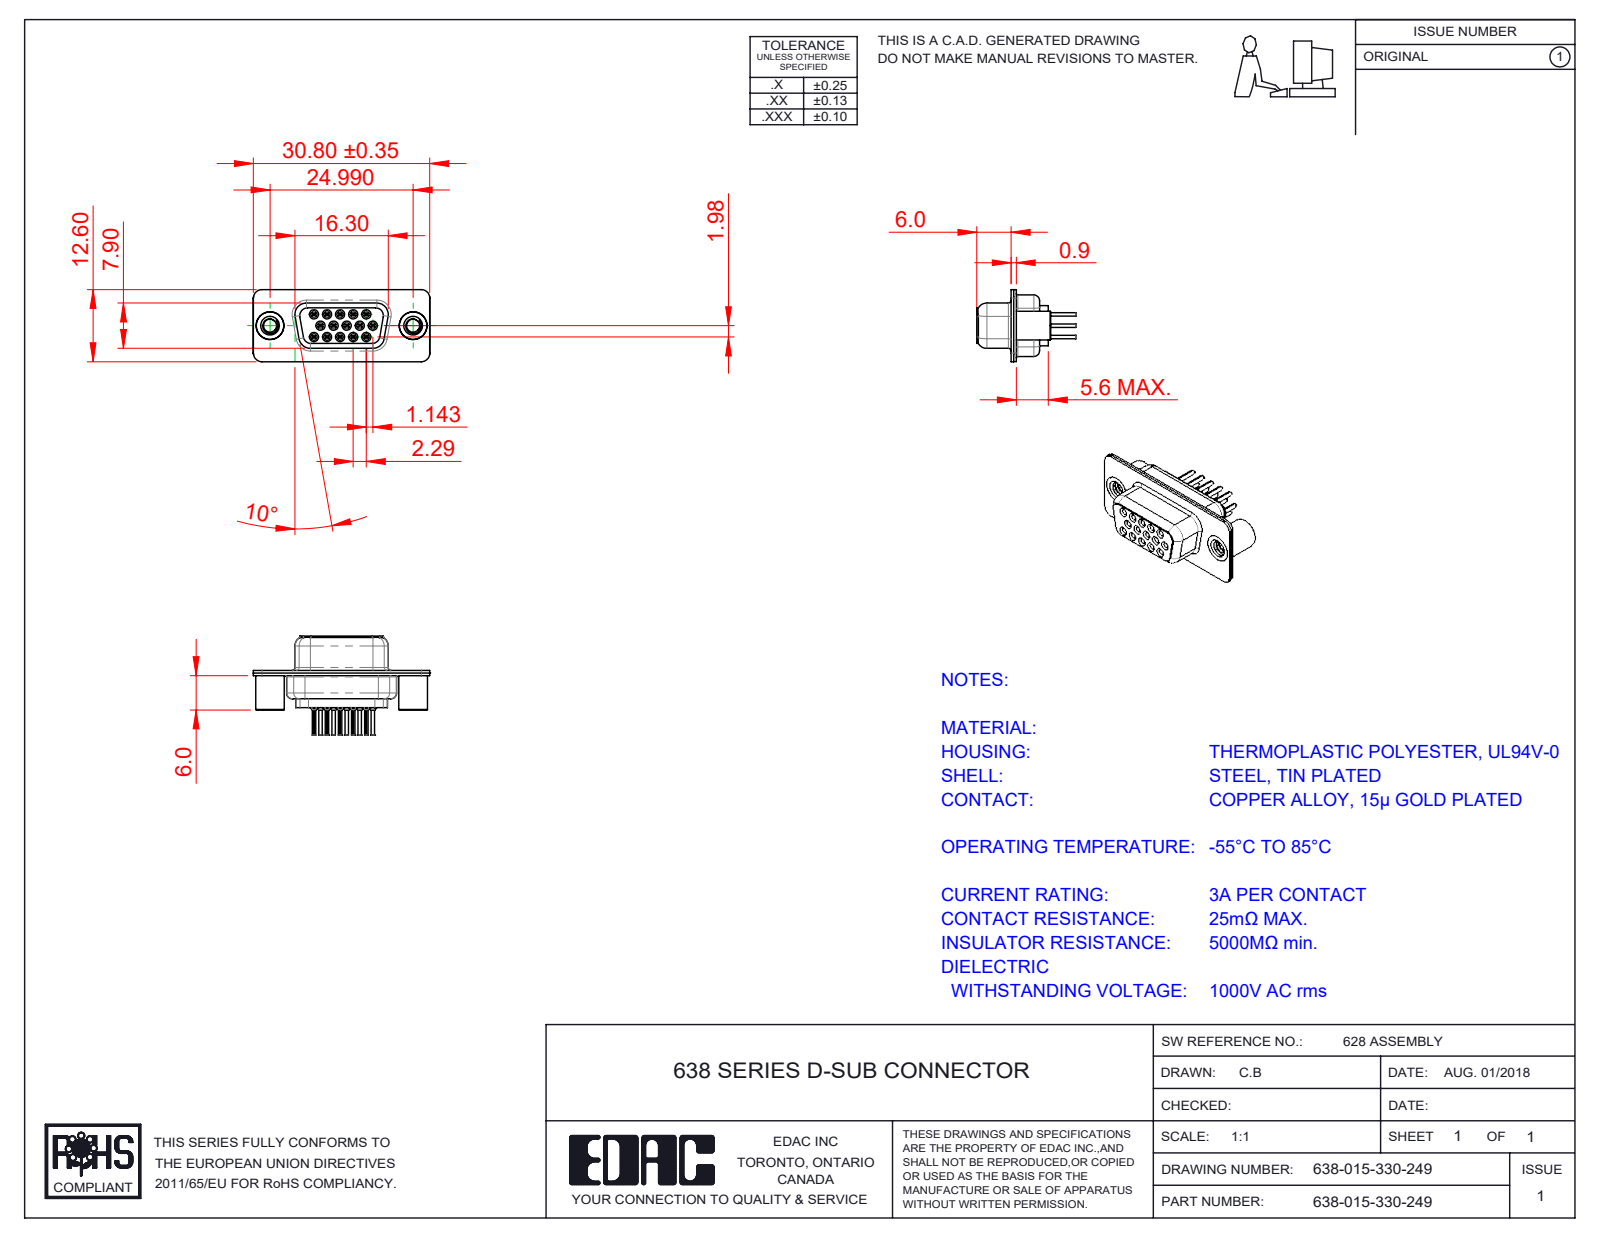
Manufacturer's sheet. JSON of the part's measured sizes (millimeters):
{"part_name": "638 4-40 Threaded Standoff BS; 638 Shell Front_15 Contacts; 638 Contact Row 2_30; 638 Contact Row 3_30 (+4 more)", "step_written_by": "SolidWorks 2020 (CONFIG_CONTROL_DESIGN)", "units": "millimeters", "bodies": {"solids": 20, "faces": 2206, "planar": 532, "cylindrical": 652, "other": 1022}, "overall_size": [30.81, 17.3, 12.6], "volume_mm3": 1672, "surface_area_mm2": 5787, "round_holes": [[0.2, 15], [0.8, 15], [1, 15], [1.1, 15], [1.6, 15], [1.7, 15], [1.8, 15], [2, 2], [2.26, 2], [4, 2], [4.05, 2], [4.85, 2]], "round_bosses_or_shafts": [[2, 15], [1.5, 15], [1.2, 15], [0.6, 15], [5, 2], [4.95, 2], [4.8, 2]], "partial_cylinders_radius": [[0.1, 30], [1.5, 20], [2, 12], [0.28, 10], [1.55, 8], [1.35, 5], [0.25, 4], [0.5, 4]], "face_to_face_distances": [0.45, 0.9, 0.4, 1.43, 8.88, 6.6, 1.4, 2.28, 0.85, 6.5], "hole_center_spacings": [3.96, 2.28, 4.57, 2.29, 6.05, 6.04, 6.86, 7.92]}
